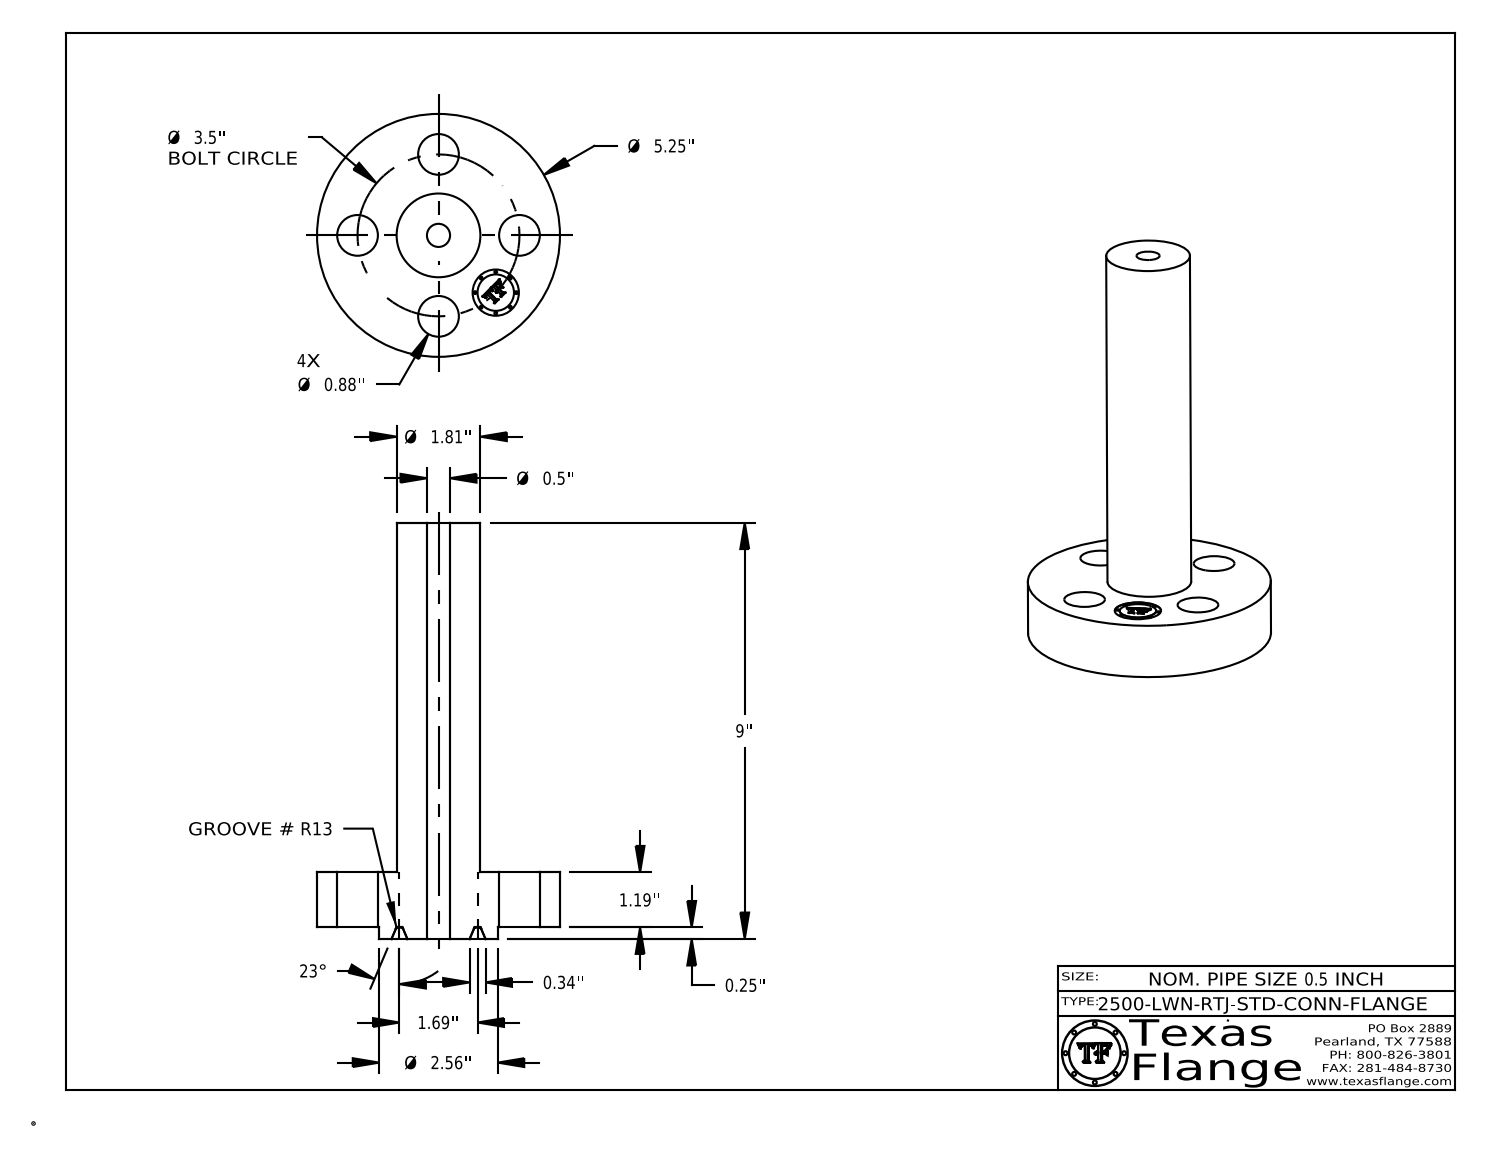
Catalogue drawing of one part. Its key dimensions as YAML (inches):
part_name: "0.5-2500-LWN-RTJ-STD-CONN-FLANGE"
step_written_by: "CATIA V5 STEP AP214 (AUTOMOTIVE_DESIGN)"
units: inches
bodies: {solids: 1, faces: 415, planar: 371, cylindrical: 36, other: 8}
overall_size: [9, 5.25, 5.25]
volume: 41.52
surface_area: 131.7
round_holes:
  - {diameter: 0.88, count: 4}
  - {diameter: 0.5, count: 1}
  - {diameter: 1, count: 1}
round_bosses_or_shafts:
  - {diameter: 0.061, count: 8}
  - {diameter: 5.25, count: 1}
  - {diameter: 2.563, count: 1}
  - {diameter: 1.81, count: 1}
  - {diameter: 0.788, count: 1}
face_to_face_distances: [1.19, 0.25, 1.44, 9, 8.75, 7.56, 1.435, 1.185, 7.565, 0.298]
hole_center_spacings: [1.75, 2.475, 1.339, 3.233, 3.5]
